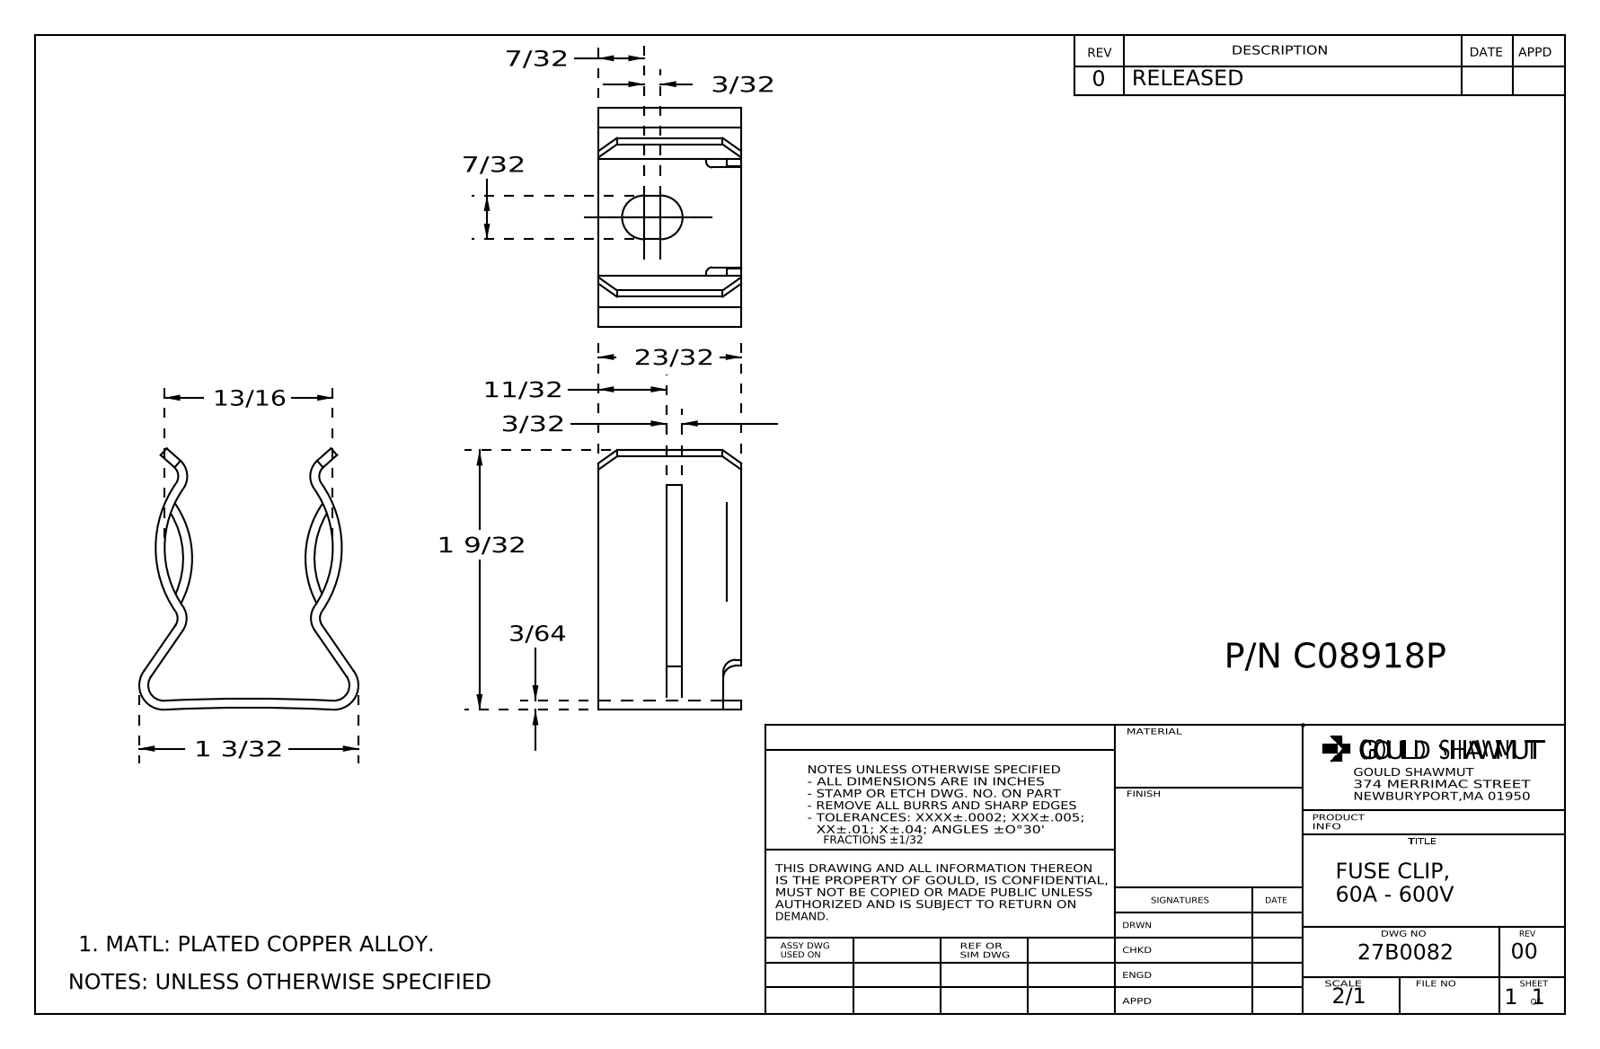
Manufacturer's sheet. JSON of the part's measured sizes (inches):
{"part_name": "27B0082rev00", "step_written_by": "SolidWorks 2013 (AUTOMOTIVE_DESIGN)", "units": "inches", "bodies": {"solids": 1, "faces": 137, "planar": 70, "cylindrical": 67, "other": 0}, "overall_size": [1.29, 1.098, 0.74], "volume_in3": 0.11, "surface_area_in2": 5.688, "partial_cylinders_radius": [[0.062, 8], [0.107, 8], [0.031, 2], [0.078, 2], [0.109, 2], [0.115, 2], [0.123, 2], [0.438, 2]], "face_to_face_distances": [0.045, 0.74, 0.4, 0.34, 0.32, 0.08, 0.42, 0.098, 0.222, 0.302]}
